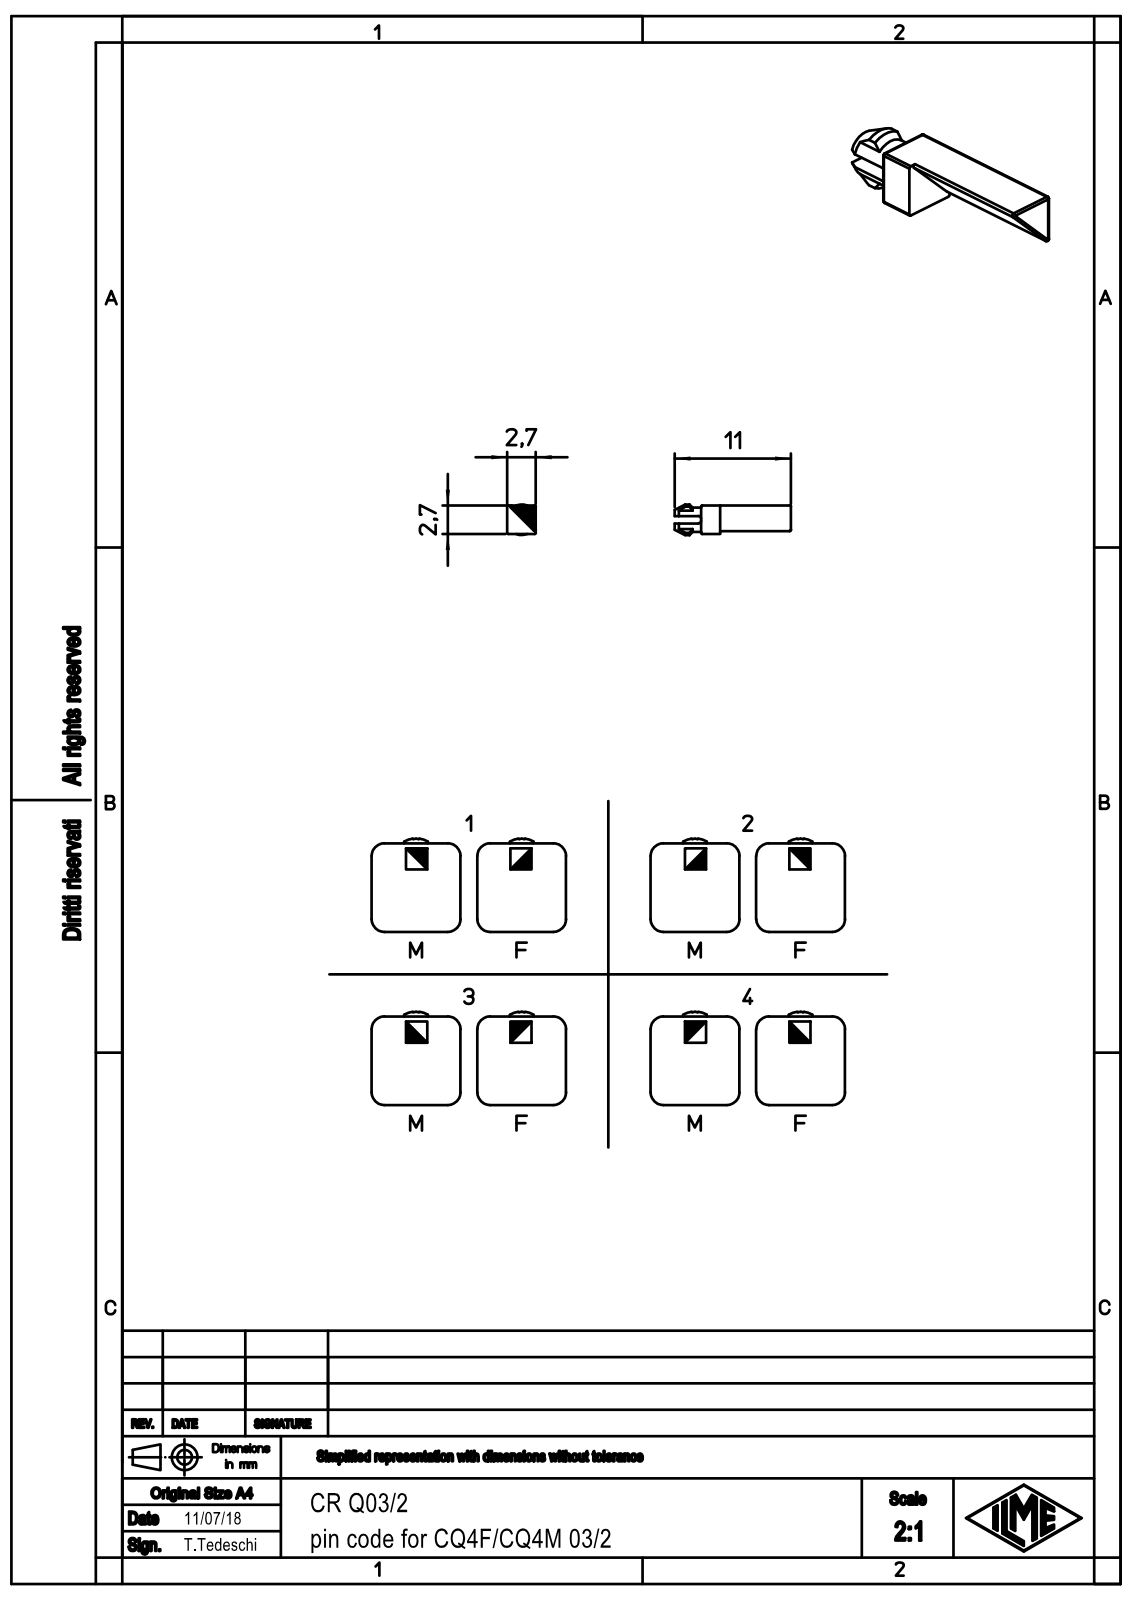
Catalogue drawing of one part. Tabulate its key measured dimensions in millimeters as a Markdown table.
| quantity | value |
| --- | --- |
| part name | CR_Q03-2 |
| STEP written by | Creo Elements/Direct Modeling 20.1B 02-Apr-2019 (C) Parametric Technology GmbH (AUTOMOTIVE_DESIGN) |
| units | millimeters |
| bodies | 1 solid, 24 faces (18 planar, 4 cylindrical, 2 other) |
| overall size | 11 × 2.9 × 2.7 |
| volume | 42 mm³ |
| surface area | 119 mm² |
| round bosses / shafts (diameter × count) | 2.3 × 1 |
| partial cylindrical surfaces (radius × count) | 1.45 × 1 |
| main face-to-face distances | 1, 1.7, 2.7, 0.7, 1.8, 6.7, 8.5, 11, 4.3, 2.5 |
